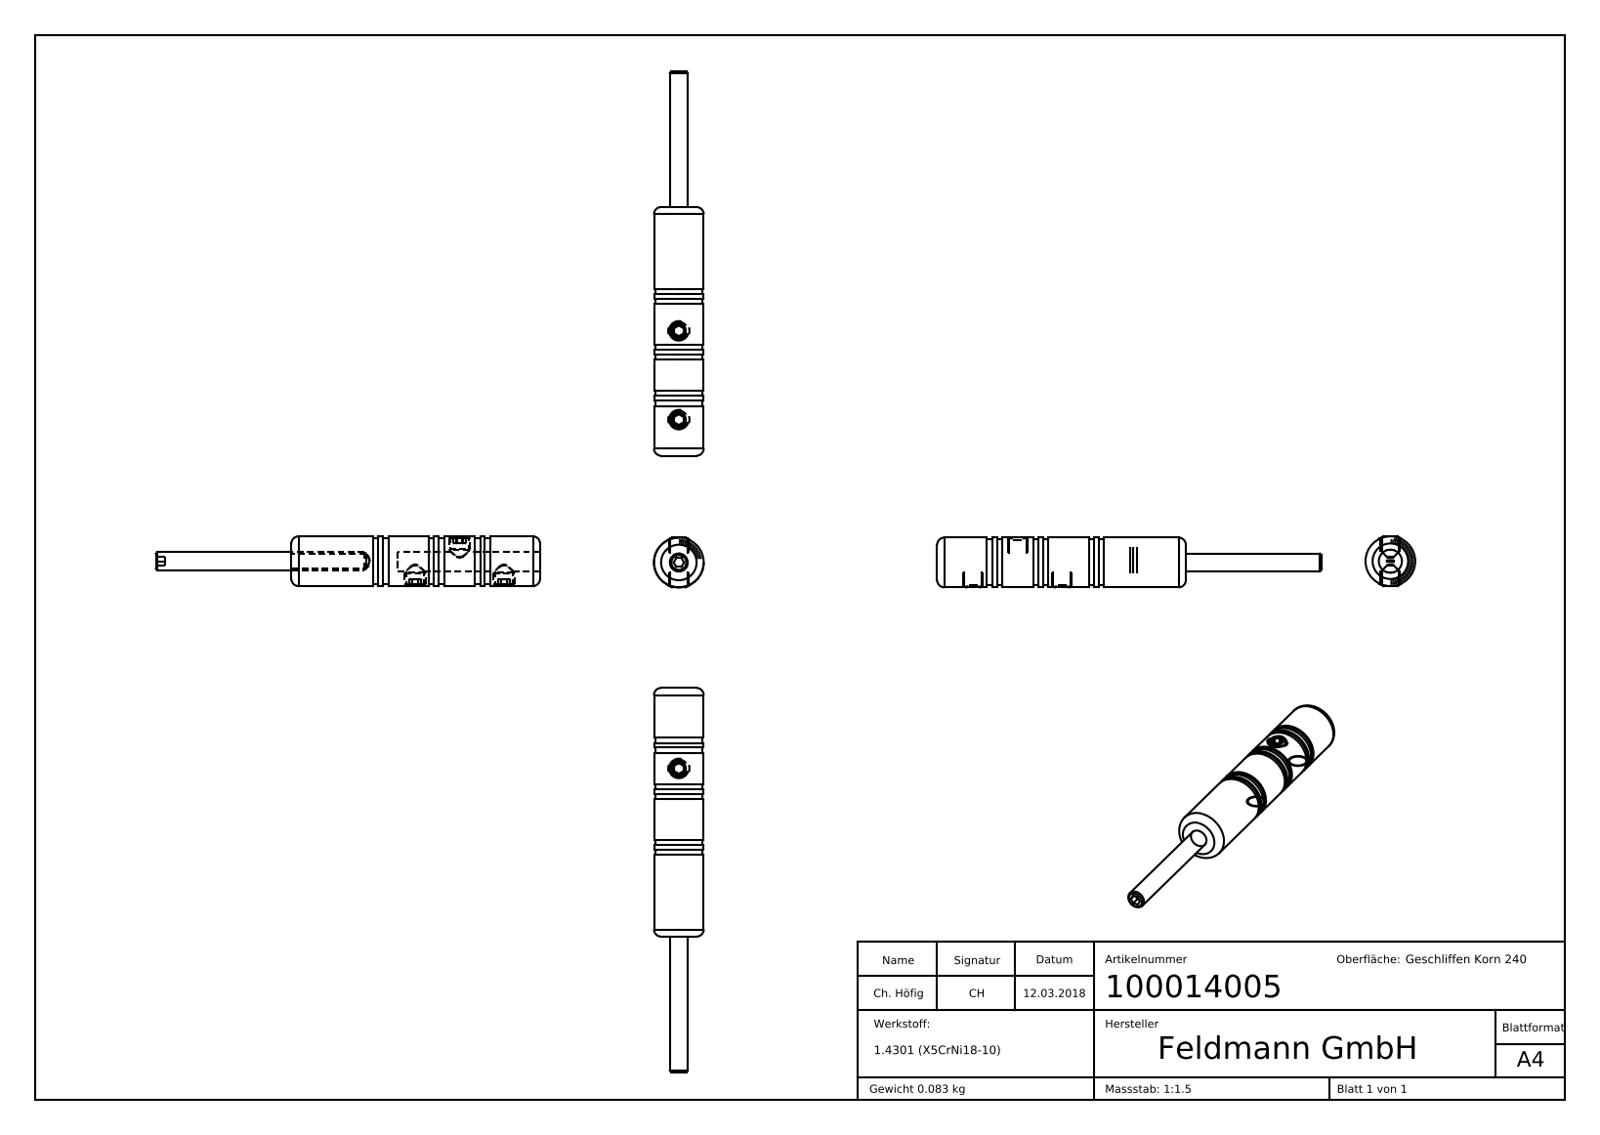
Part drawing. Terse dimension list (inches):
name: DIN913_DIN913 M5x60; 100014005; DIN914_DIN 914 M6x6; 10001X00X Teil 1_100014005 Teil1
written by: SolidWorks 2015 (CONFIG_CONTROL_DESIGN)
unit: in
bodies: 5 solids, 431 faces (162 planar, 98 cylindrical, 171 other)
size: 4.258 × 0.551 × 0.551
volume: 0.641 in³; area: 9.347 in²
holes: 3× ⌀0.197, 1× ⌀0.165, 1× ⌀0.217
bosses: 3× ⌀0.236, 1× ⌀0.551, 1× ⌀0.512, 1× ⌀0.197
rounds: 50× R0.008
face distances: 0.059, 0.11, 0.512, 0.618, 1.13, 0.051, 0.402, 0.453, 0.169, 2.756
hole spacings: 0.492, 0.984
